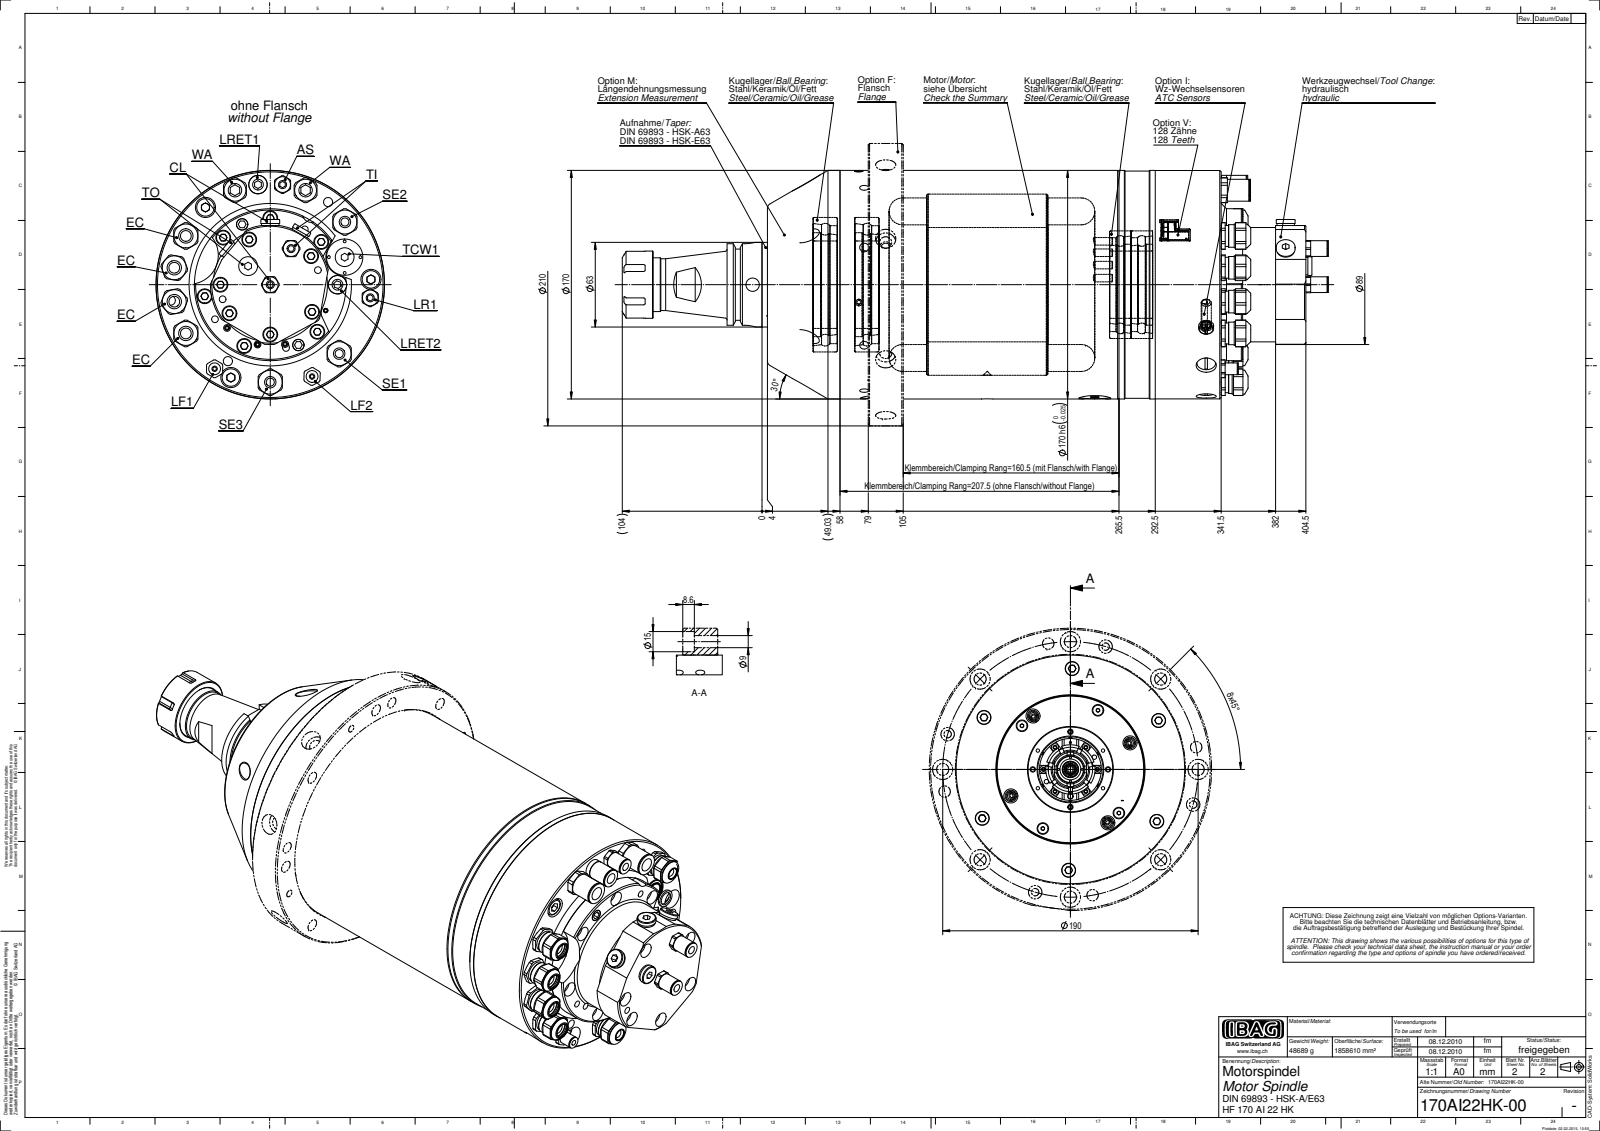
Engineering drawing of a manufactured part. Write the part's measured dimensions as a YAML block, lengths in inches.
part_name: "170AI22HK-00"
step_written_by: "SolidWorks 2012 (CONFIG_CONTROL_DESIGN)"
units: inches
bodies: {solids: 0, faces: 1453, planar: 591, cylindrical: 564, other: 298}
overall_size: [20.694, 6.693, 6.693]
round_holes:
  - {diameter: 0.268, count: 19}
  - {diameter: 0.433, count: 12}
  - {diameter: 0.335, count: 8}
  - {diameter: 0.197, count: 7}
  - {diameter: 0.236, count: 7}
  - {diameter: 0.591, count: 7}
  - {diameter: 0.315, count: 6}
  - {diameter: 0.409, count: 6}
  - {diameter: 0.083, count: 4}
  - {diameter: 0.177, count: 4}
  - {diameter: 0.394, count: 4}
  - {diameter: 0.421, count: 4}
round_bosses_or_shafts:
  - {diameter: 0.701, count: 7}
  - {diameter: 0.661, count: 7}
  - {diameter: 0.614, count: 7}
  - {diameter: 0.512, count: 7}
  - {diameter: 0.551, count: 5}
  - {diameter: 0.461, count: 4}
  - {diameter: 0.394, count: 4}
  - {diameter: 0.301, count: 4}
partial_cylinders:
  - {radius: 0.039, count: 12}
  - {radius: 0.39, count: 7}
  - {radius: 0.26, count: 6}
  - {radius: 0.315, count: 4}
  - {radius: 0.098, count: 2}
  - {radius: 0.276, count: 2}
  - {radius: 0.364, count: 2}
  - {radius: 0.256, count: 1}
face_to_face_distances: [9.232, 11.161, 1.929, 2.126, 11.358, 13.287, 15.768, 13.642, 4.409, 2.48]
hole_center_spacings: [2.953, 0.63, 5.115, 0.654, 5.008, 0.694, 0.925, 1.102]
